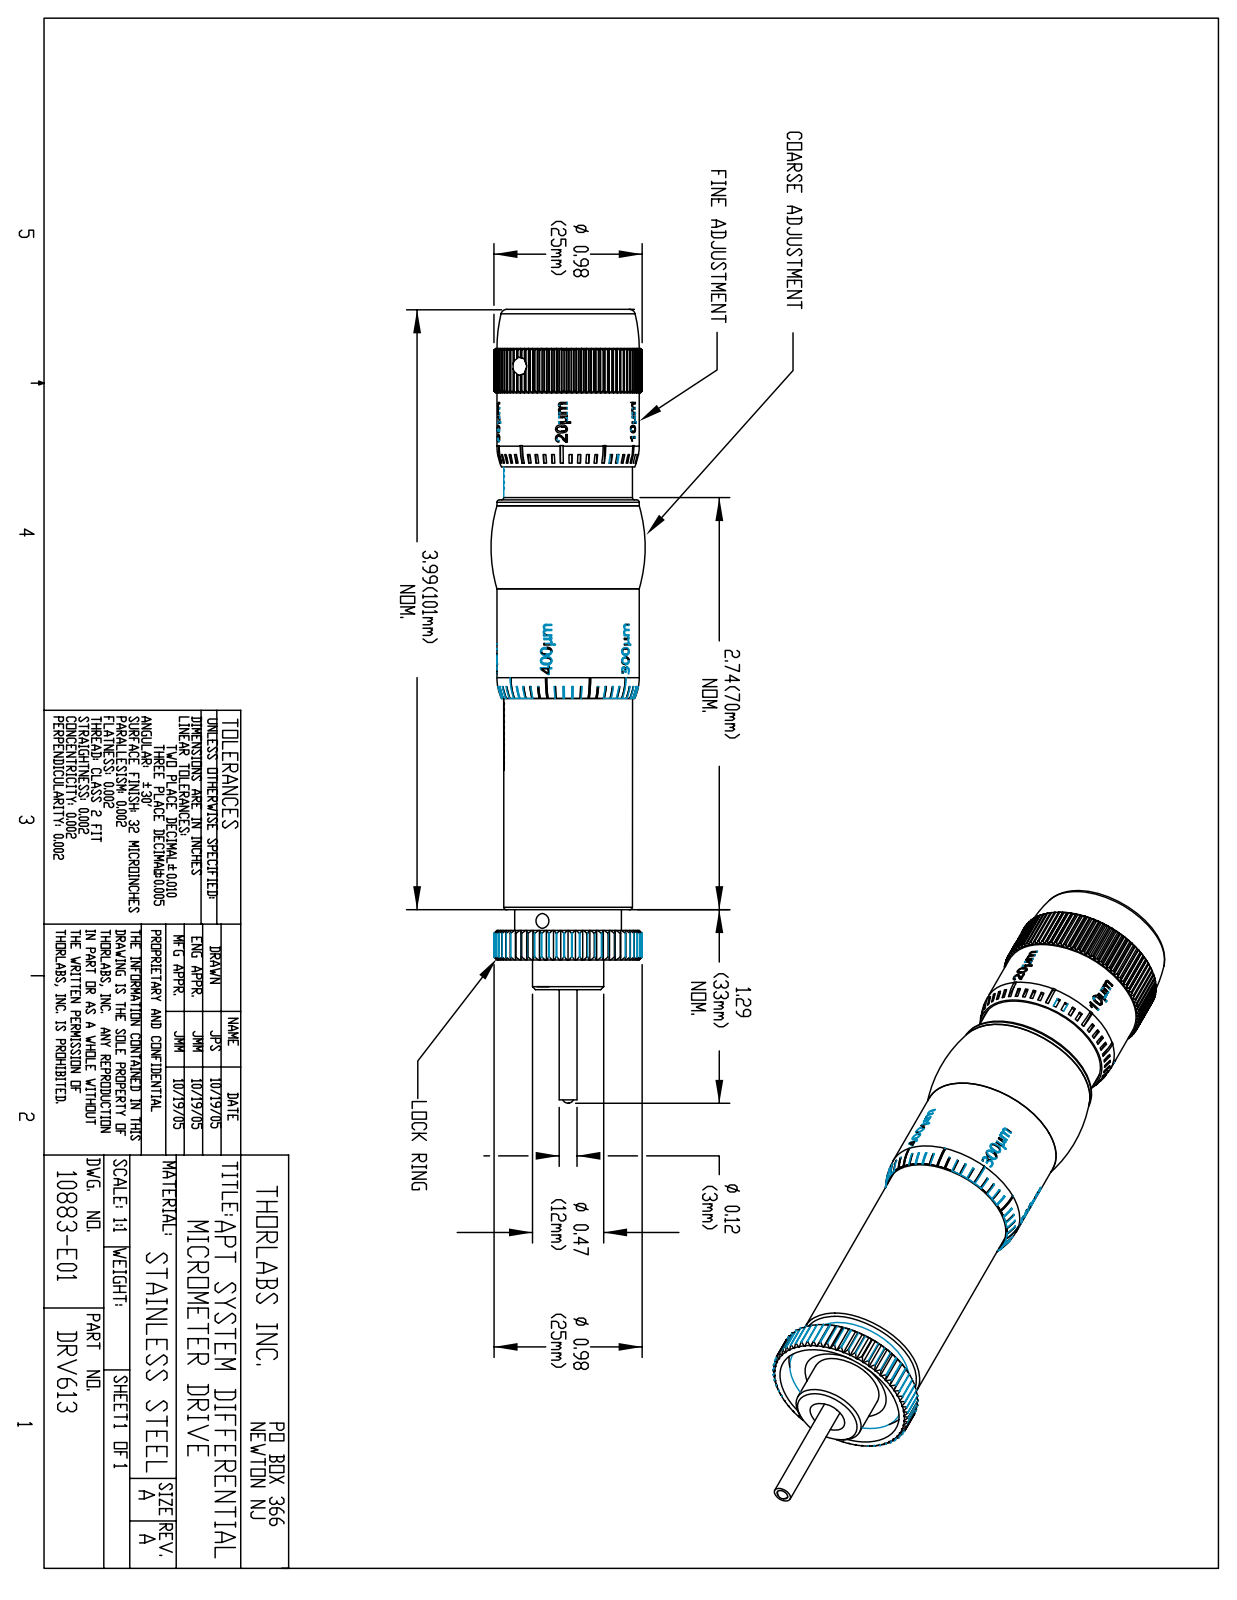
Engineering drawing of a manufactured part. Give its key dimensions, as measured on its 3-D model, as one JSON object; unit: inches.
{"part_name": "10883-E0W", "step_written_by": "SolidWorks 2007 (AUTOMOTIVE_DESIGN)", "units": "inches", "bodies": {"solids": 0, "faces": 1409, "planar": 667, "cylindrical": 265, "other": 477}, "overall_size": [5.275, 1.024, 1.024], "round_holes": [[0.078, 1], [0.098, 1], [0.118, 1], [0.252, 1], [0.866, 1]], "round_bosses_or_shafts": [[0.945, 1], [0.854, 1], [0.709, 1], [0.472, 1], [0.118, 1]], "partial_cylinders_radius": [[0.427, 1], [0.453, 1], [0.471, 1], [0.492, 1]], "face_to_face_distances": [0.098, 0.051, 0.047, 0.661, 0.197, 0.679, 0.661, 0.236, 0.189, 0.138]}
